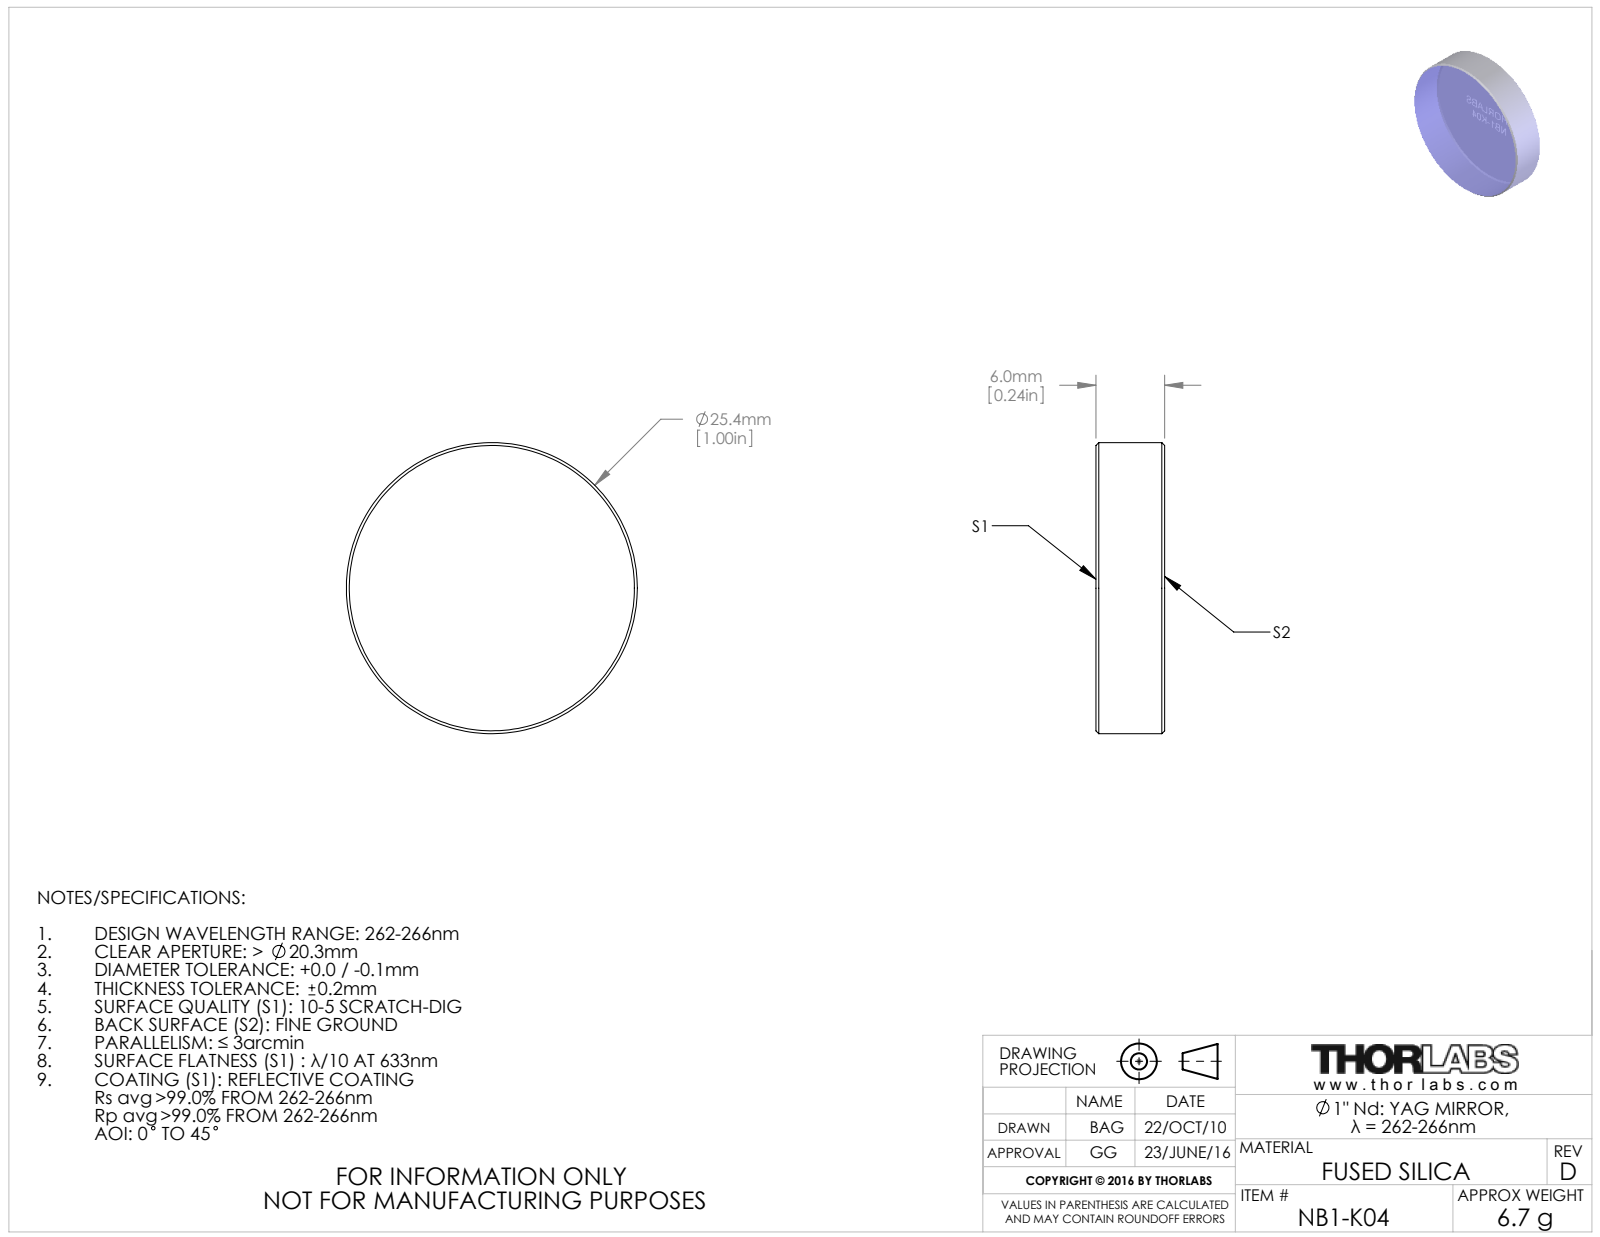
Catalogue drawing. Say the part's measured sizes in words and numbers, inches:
The part is named "19189-E0W". Its 3-D file was written by "SolidWorks 2016 (CONFIG_CONTROL_DESIGN)". It is 1 solid with 209 faces: 139 planar, 2 cylindrical and 68 other. Overall it measures 1 by 1 by 0.236 inches. Its volume is 0.185 cubic inches and its surface area 2.276 square inches. Round bosses or shafts: 1 of diameter 1. The main face-to-face distances are 0.236, 0.061, 0.094, 0.093, 0.038, 0.163, 0.144, 0.043, 0.07, 0.076.
